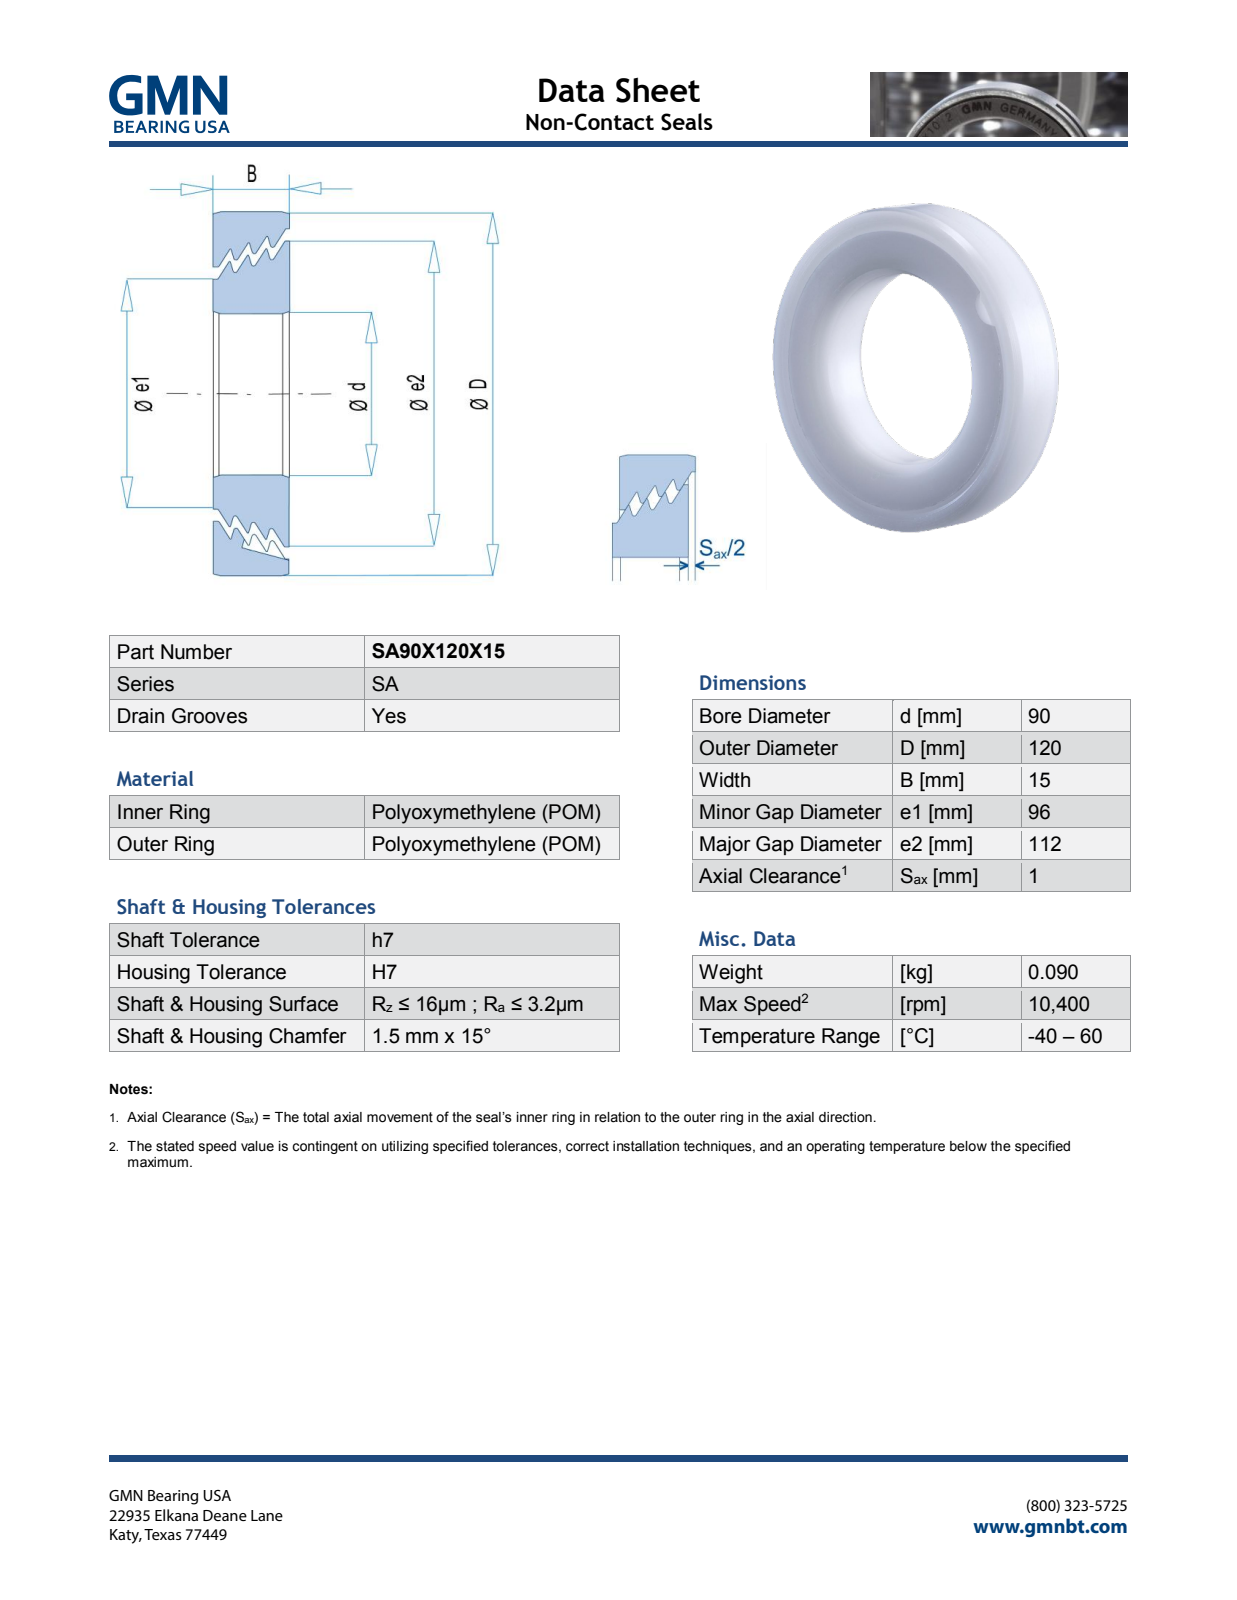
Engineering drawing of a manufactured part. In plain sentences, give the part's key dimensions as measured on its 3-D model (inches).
The part is named "SA90X120X15_PRT". Its 3-D file was written by "PRO/ENGINEER BY PARAMETRIC TECHNOLOGY CORPORATION, 2013150 (AUTOMOTIVE_DESIGN)". It is 2 solids with 698 faces: 613 planar, 13 cylindrical and 72 other. Overall it measures 4.724 by 4.724 by 0.593 inches. Its volume is 4.185 cubic inches and its surface area 56.76 square inches. Round holes: 1 of diameter 3.543, 1 of diameter 3.844, 1 of diameter 4.474. Round bosses or shafts: 1 of diameter 4.724, 1 of diameter 4.409, 1 of diameter 3.78. Partial cylindrical surfaces (rounded edges, fillets, slot ends): 1 of radius 0.236. The main face-to-face distances are 0.591, 0.593, 0.365, 0.362, 0.229, 0.085, 0.074, 0.084, 0.06, 0.063.
